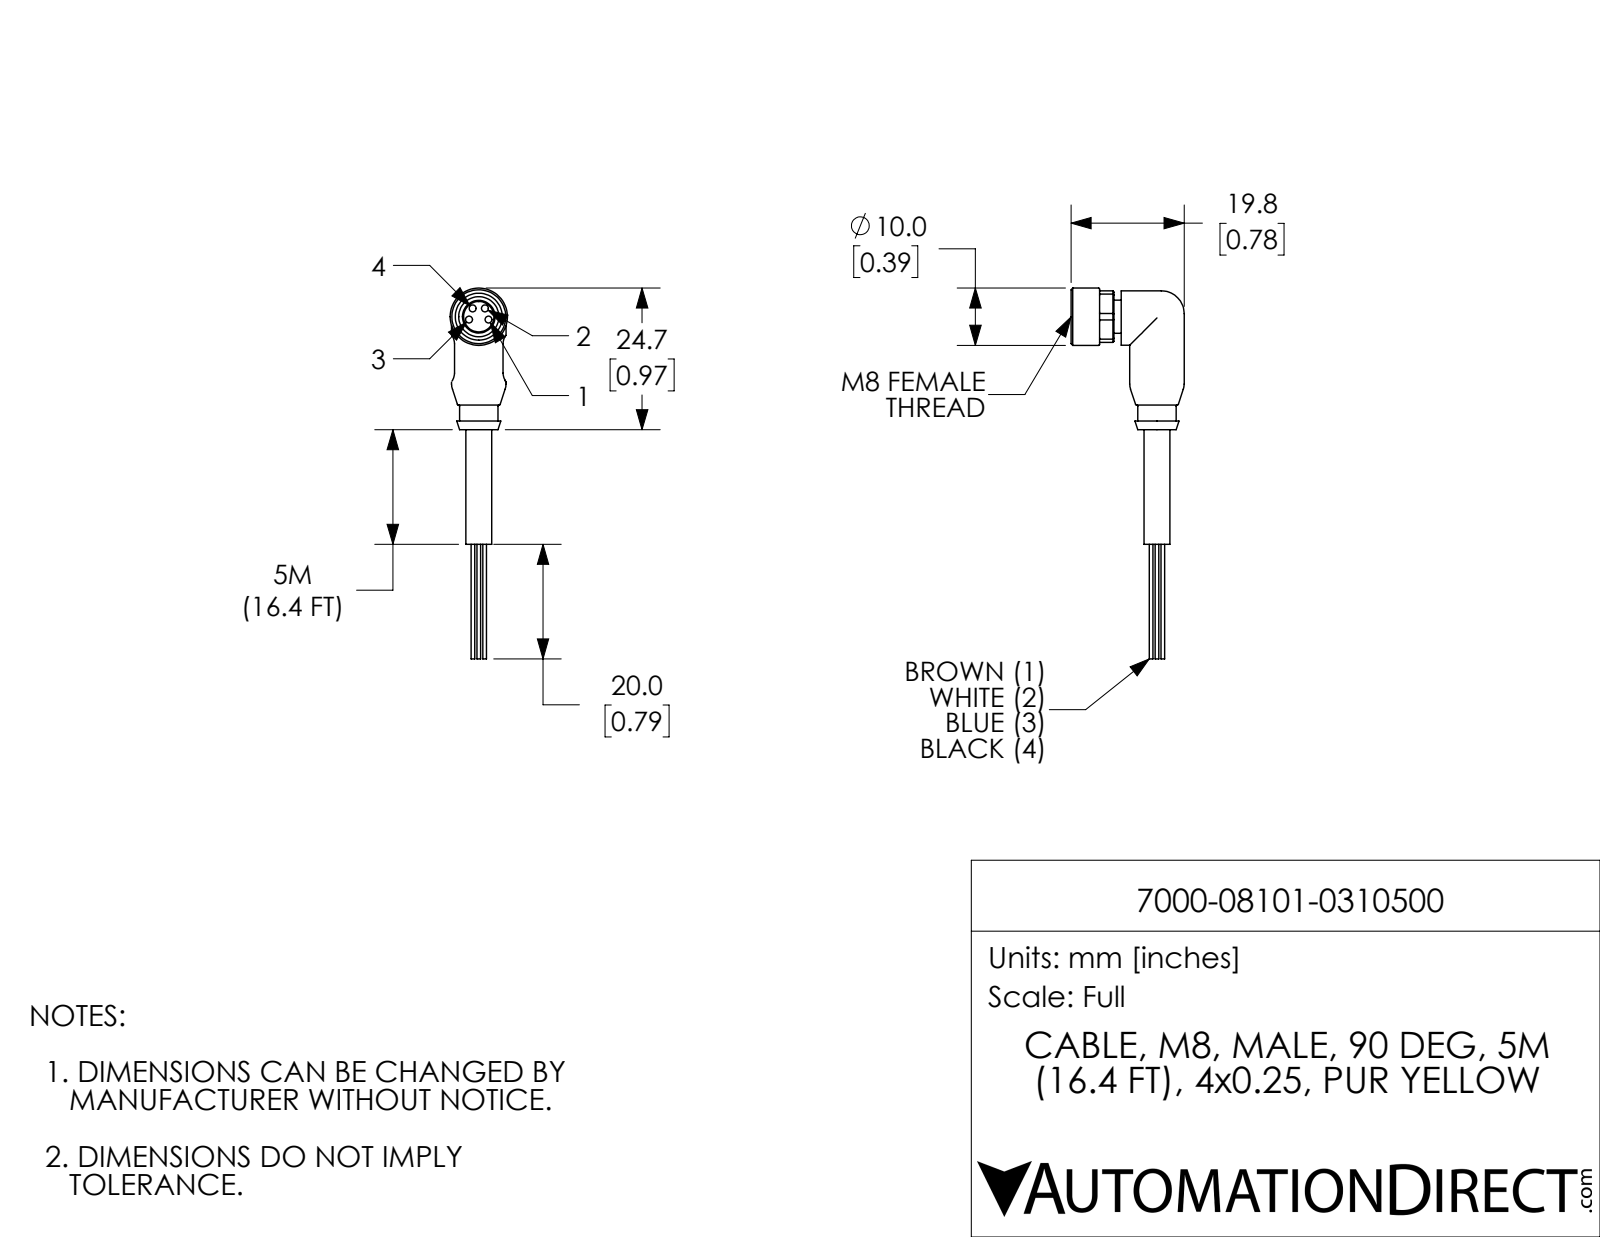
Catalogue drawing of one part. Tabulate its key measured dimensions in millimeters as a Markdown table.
| quantity | value |
| --- | --- |
| part name | 7000-08101-0310500 |
| STEP written by | SolidWorks 2021 (CONFIG_CONTROL_DESIGN) |
| units | millimeters |
| bodies | 5 solids, 117 faces (41 planar, 47 cylindrical, 29 other) |
| overall size | 64.7 × 19.8 × 10 |
| volume | 2 410 mm³ |
| surface area | 1 920 mm² |
| round holes (diameter × count) | 1.2 × 4, 7 × 1 |
| round bosses / shafts (diameter × count) | 0.6 × 3, 9.5 × 2, 10 × 1, 6.7 × 1, 5.8 × 1, 5.7 × 1, 4.5 × 1, 0.6 × 1 |
| partial cylindrical surfaces (radius × count) | 0.2 × 4, 2.5 × 4, 4.9 × 1 |
| main face-to-face distances | 1.2, 9, 1.5, 8.5, 0.7, 20, 6.8, 8.1, 7.5, 8.7 |
| hole center spacings | 1.8, 1.8, 2.1, 3.4, 2.1, 3.4 |
